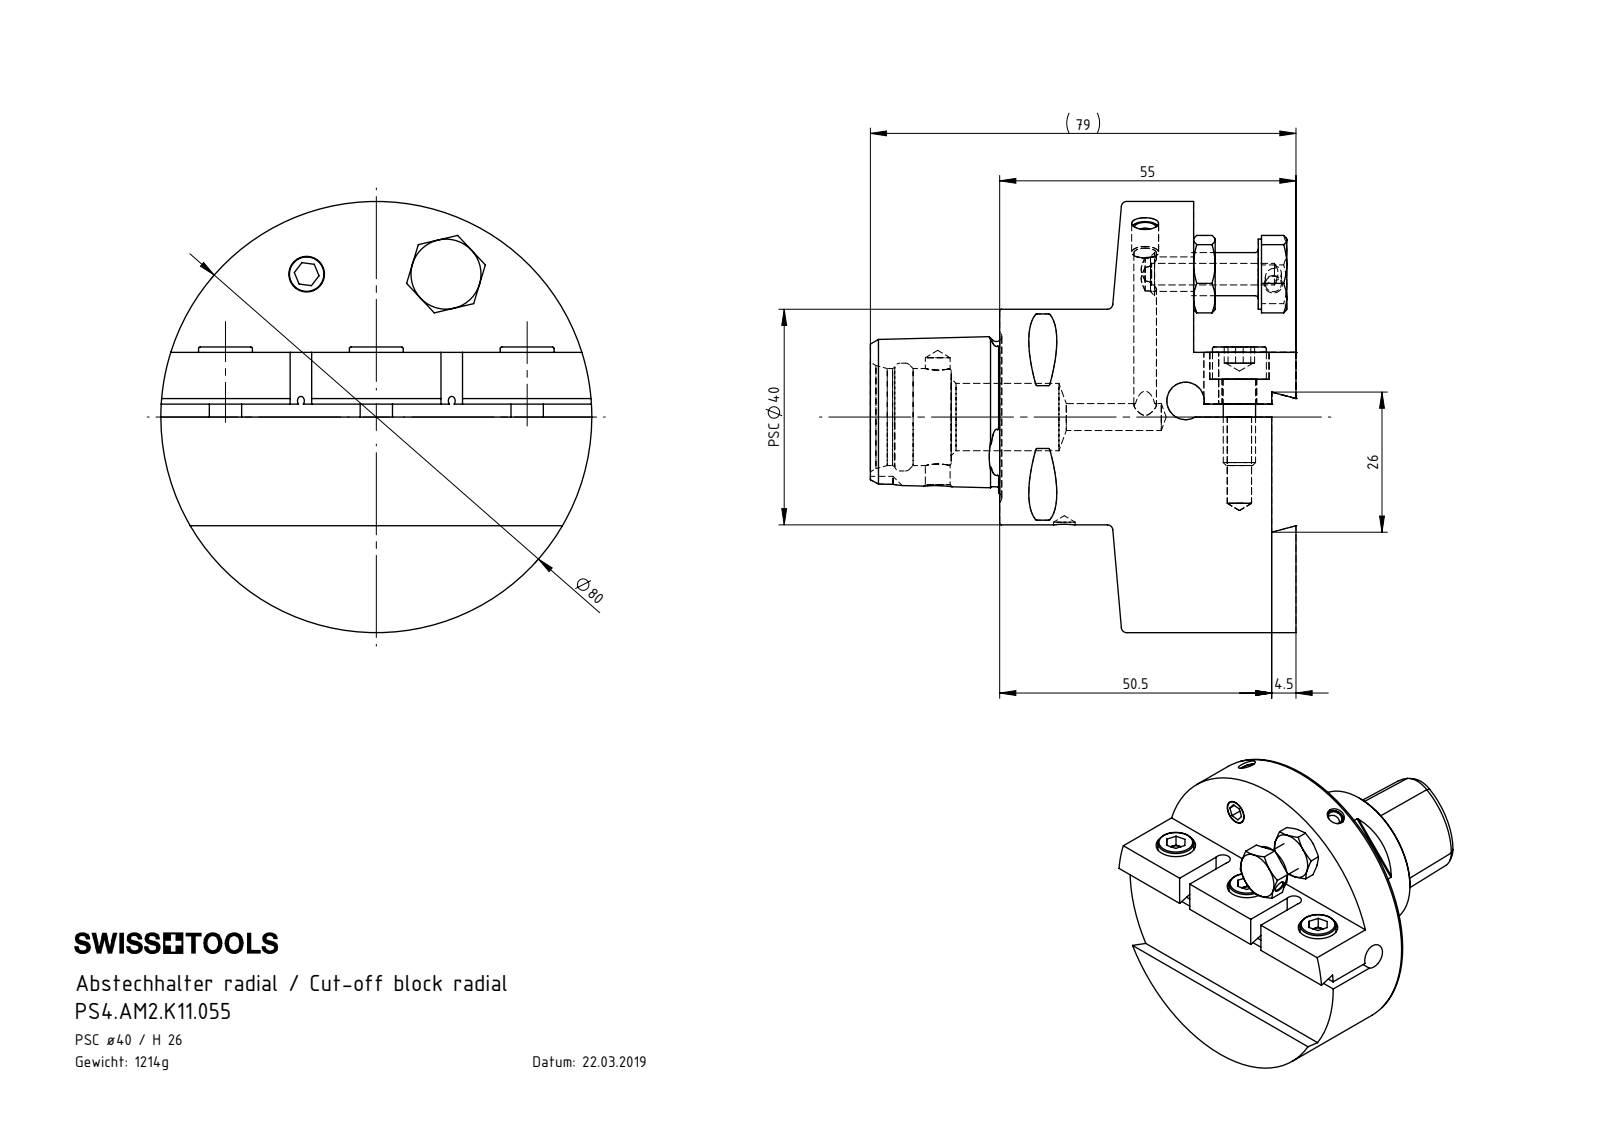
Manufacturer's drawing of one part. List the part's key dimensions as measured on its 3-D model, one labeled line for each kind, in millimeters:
Part name (STEP PRODUCT): PS4.AM2.K11.055; AM3-ER1.001.020_PreviewCfg; ISO 4035 - M8_PreviewCfg; KVT_MB_600_050 (+3 more)
STEP written by: SolidWorks 2017 (AUTOMOTIVE_DESIGN)
Units: millimetres
Bodies: 11 solids, 309 faces (124 planar, 55 cylindrical, 130 other)
Overall size (bounding box): 80 × 80 × 79
Volume: 155 804 mm³ · Surface area: 35 756 mm²
Round holes (diameter × count): ⌀6.4 ×5, ⌀4 ×4, ⌀4.5 ×3, ⌀5 ×3, ⌀11 ×3, ⌀4.2 ×2, ⌀7 ×2, ⌀3 ×1, ⌀4.6 ×1, ⌀12.5 ×1, ⌀18 ×1, ⌀20 ×1
Round bosses / shafts (diameter × count): ⌀10 ×3, ⌀6 ×3, ⌀8 ×2, ⌀5 ×2, ⌀80 ×1, ⌀40 ×1, ⌀13 ×1
Partial cylindrical surfaces — rounded edges, fillets, slot ends (radius × count): R0.3 ×8, R2.1 ×2, R3 ×1
Main face-to-face distances: 14.5, 19, 4.5, 12, 2.4, 9.6, 55, 36, 50.5, 7
Hole centre spacings: 28, 29.5, 42.9, 56, 62.61, 23.5, 25.86, 32.5
